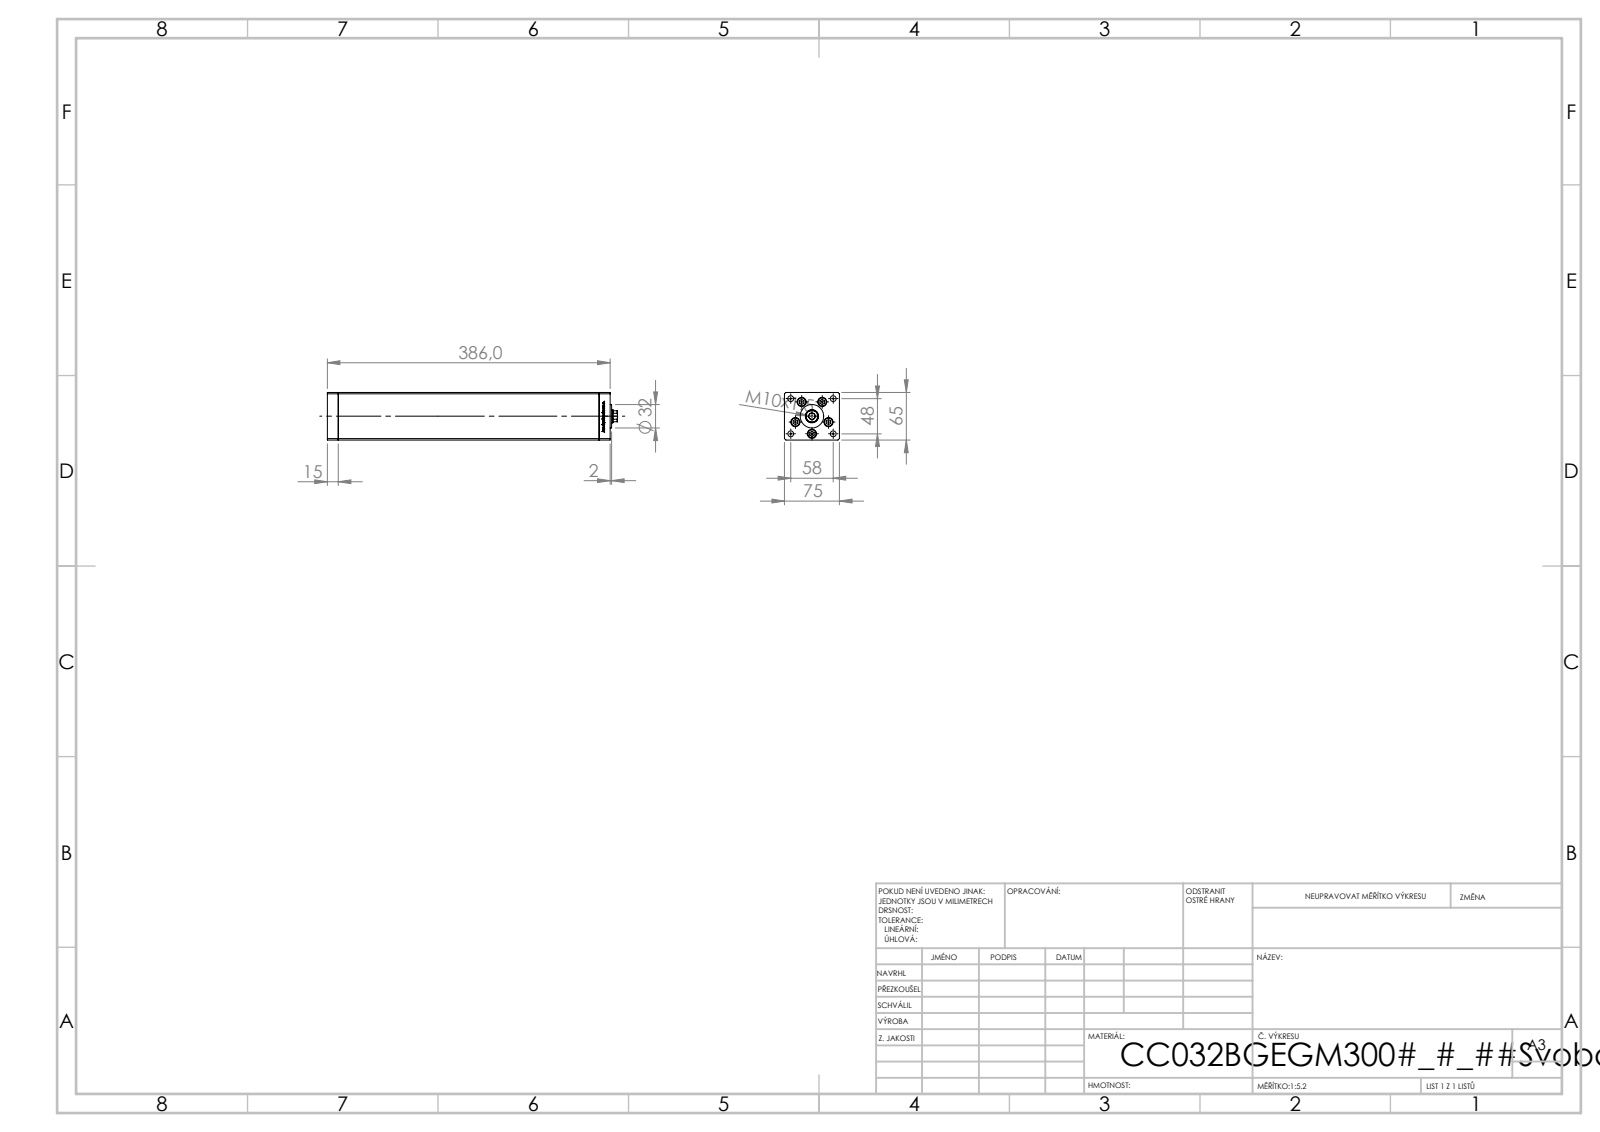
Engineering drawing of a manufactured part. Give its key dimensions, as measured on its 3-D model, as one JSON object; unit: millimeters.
{"part_name": "V220C_B MIDDLE; V220C BACK_B; V220C_FRONT_B; V220C_VC_B (+1 more)", "step_written_by": "SolidWorks 2019 (CONFIG_CONTROL_DESIGN)", "units": "millimeters", "bodies": {"solids": 14, "faces": 1183, "planar": 462, "cylindrical": 147, "other": 574}, "overall_size": [396, 75, 65], "volume_mm3": 1630000, "surface_area_mm2": 227835, "round_holes": [[9, 5], [12.5, 5], [8, 4], [2, 2], [13.16, 2], [8.5, 1], [18, 1]], "round_bosses_or_shafts": [[8, 5], [32, 1]], "partial_cylinders_radius": [[0.93, 2], [8.5, 1]], "face_to_face_distances": [75, 65, 15, 356, 371, 54.5, 10.5, 26.25, 48.75, 4], "hole_center_spacings": [24, 37.64, 15.67, 17.22, 27.71, 28.83, 29, 32.63]}
